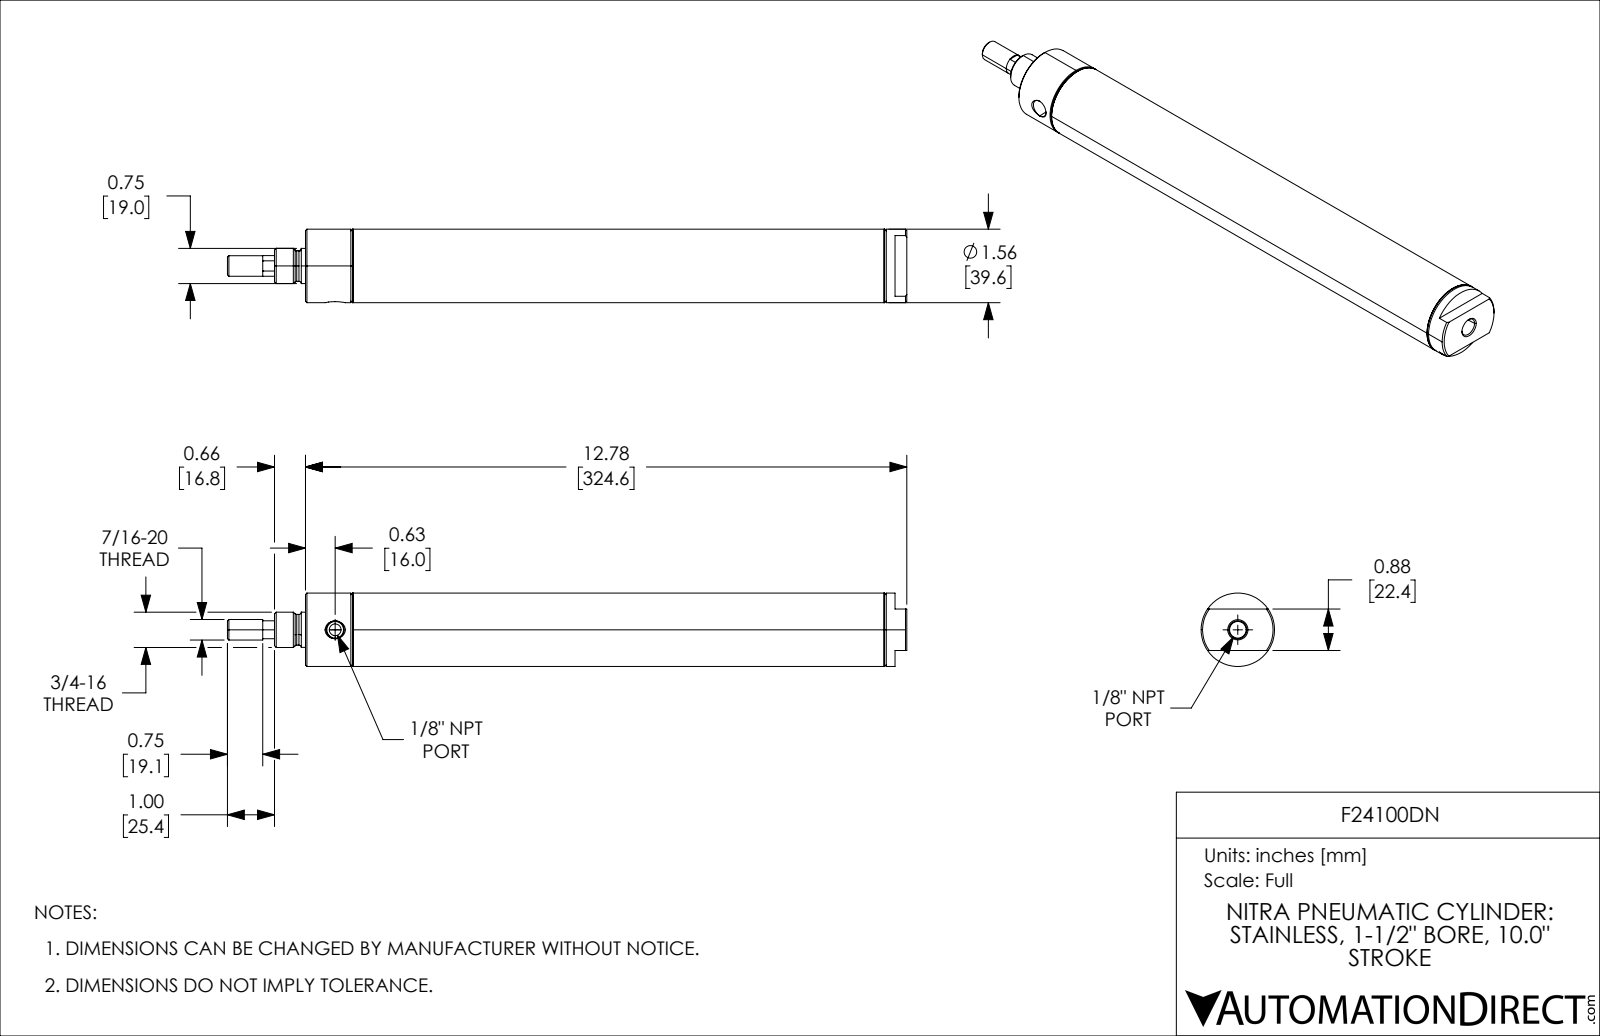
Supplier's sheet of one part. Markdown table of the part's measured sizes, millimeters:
| quantity | value |
| --- | --- |
| part name | F24100DN_7; F24100DN_9; F24100DN; F24100DN_3 (+1 more) |
| STEP written by | SolidWorks 2021 (CONFIG_CONTROL_DESIGN) |
| units | millimeters |
| bodies | 4 solids, 126 faces (28 planar, 42 cylindrical, 56 other) |
| overall size | 366.73 × 39.62 × 39.62 |
| volume | 129 851 mm³ |
| surface area | 102 622 mm² |
| round holes (diameter × count) | 6.35 × 1, 11.73 × 1, 24.71 × 1, 36.36 × 1 |
| round bosses / shafts (diameter × count) | 39.62 × 1, 38.39 × 1, 19.05 × 1, 18.99 × 1, 16.6 × 1, 11.13 × 1, 11.11 × 1 |
| main face-to-face distances | 22.22, 6.35, 11.13, 254, 276.22, 30.86, 284.86, 307.08, 324.56, 293.7 |
